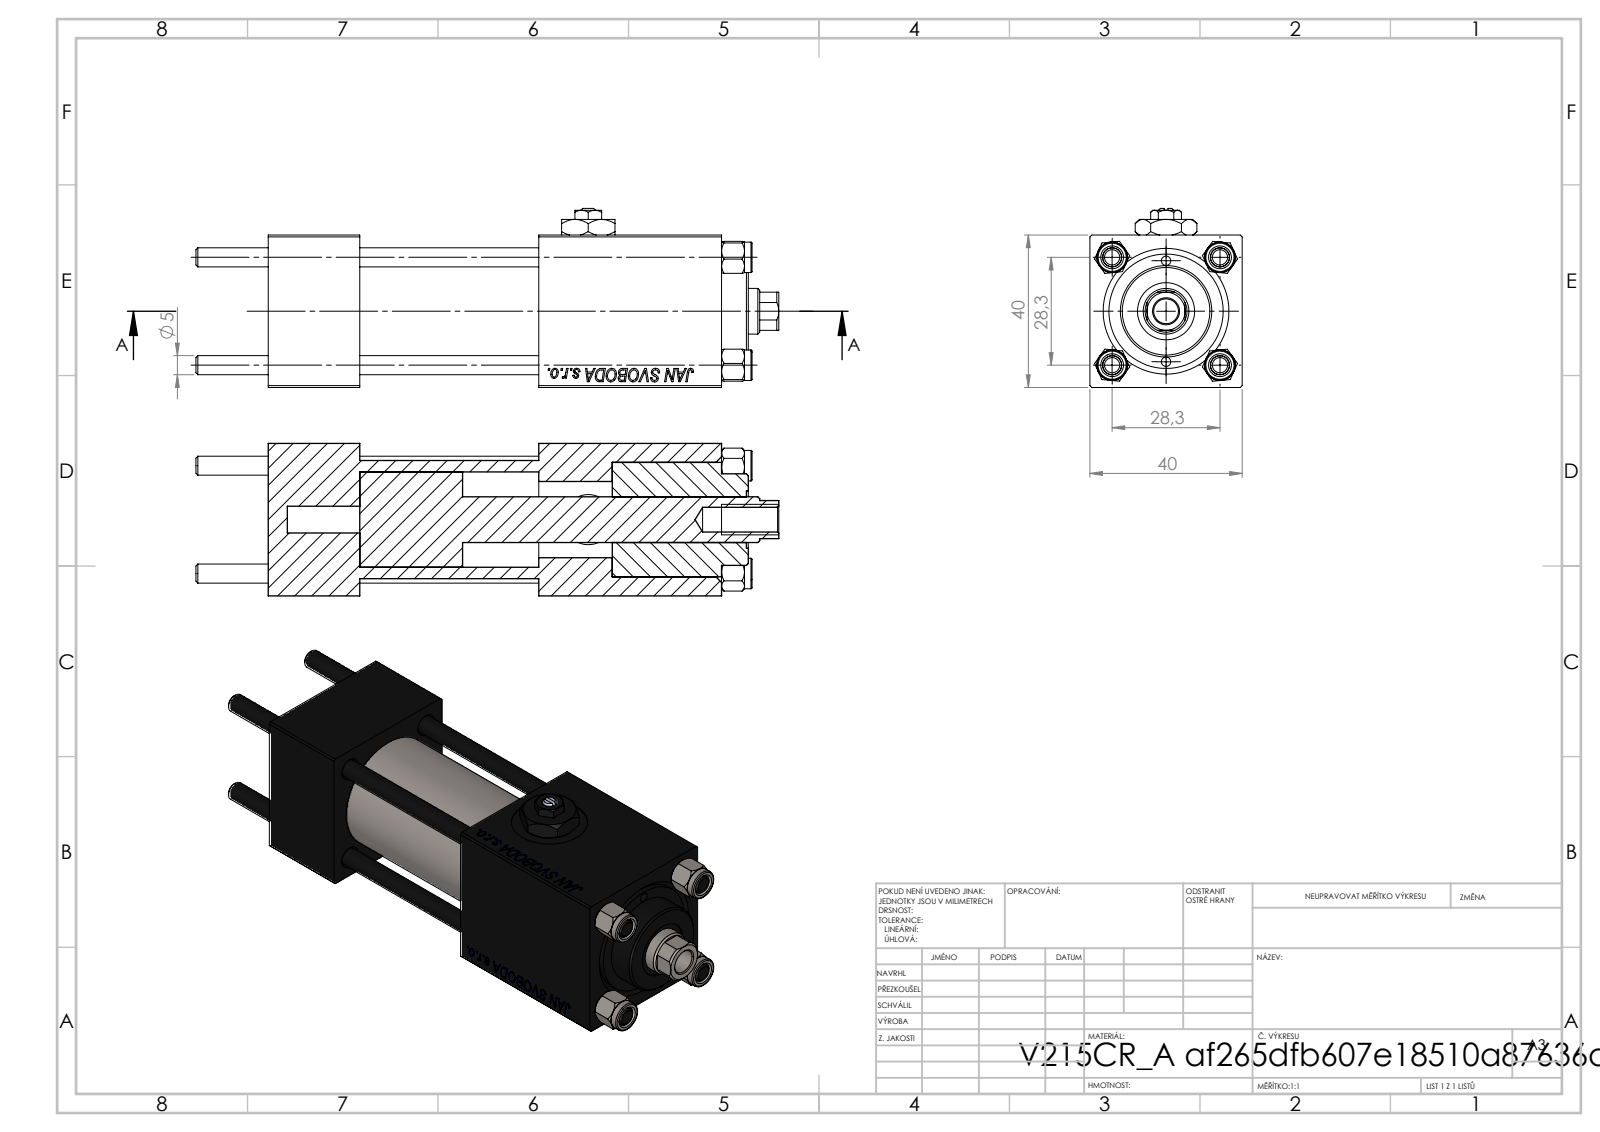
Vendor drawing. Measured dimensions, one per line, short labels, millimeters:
name: NUT_M5; CR025_012_A_0_G_A_G_M_020_+#_##_TYCINKA; V215_VC_A; V215CR_BODY_A (+2 more)
written by: SolidWorks 2019 (CONFIG_CONTROL_DESIGN)
unit: mm
bodies: 12 solids, 1185 faces (543 planar, 86 cylindrical, 556 other)
size: 153 × 47 × 40
volume: 144 124 mm³; area: 59 693 mm²
holes: 4× ⌀5, 3× ⌀20, 2× ⌀2.5, 2× ⌀7, 2× ⌀13.16, 1× ⌀6.5, 1× ⌀12, 1× ⌀15, 1× ⌀25, 1× ⌀30
bosses: 4× ⌀8, 1× ⌀31, 1× ⌀24
rounds: 1× R5.5
face distances: 40, 24, 119, 95, 90.3, 66.3, 28.7, 47, 48, 71
hole spacings: 14.18, 20.01, 28.3, 30.84, 13.25, 40.02, 26.5, 72
